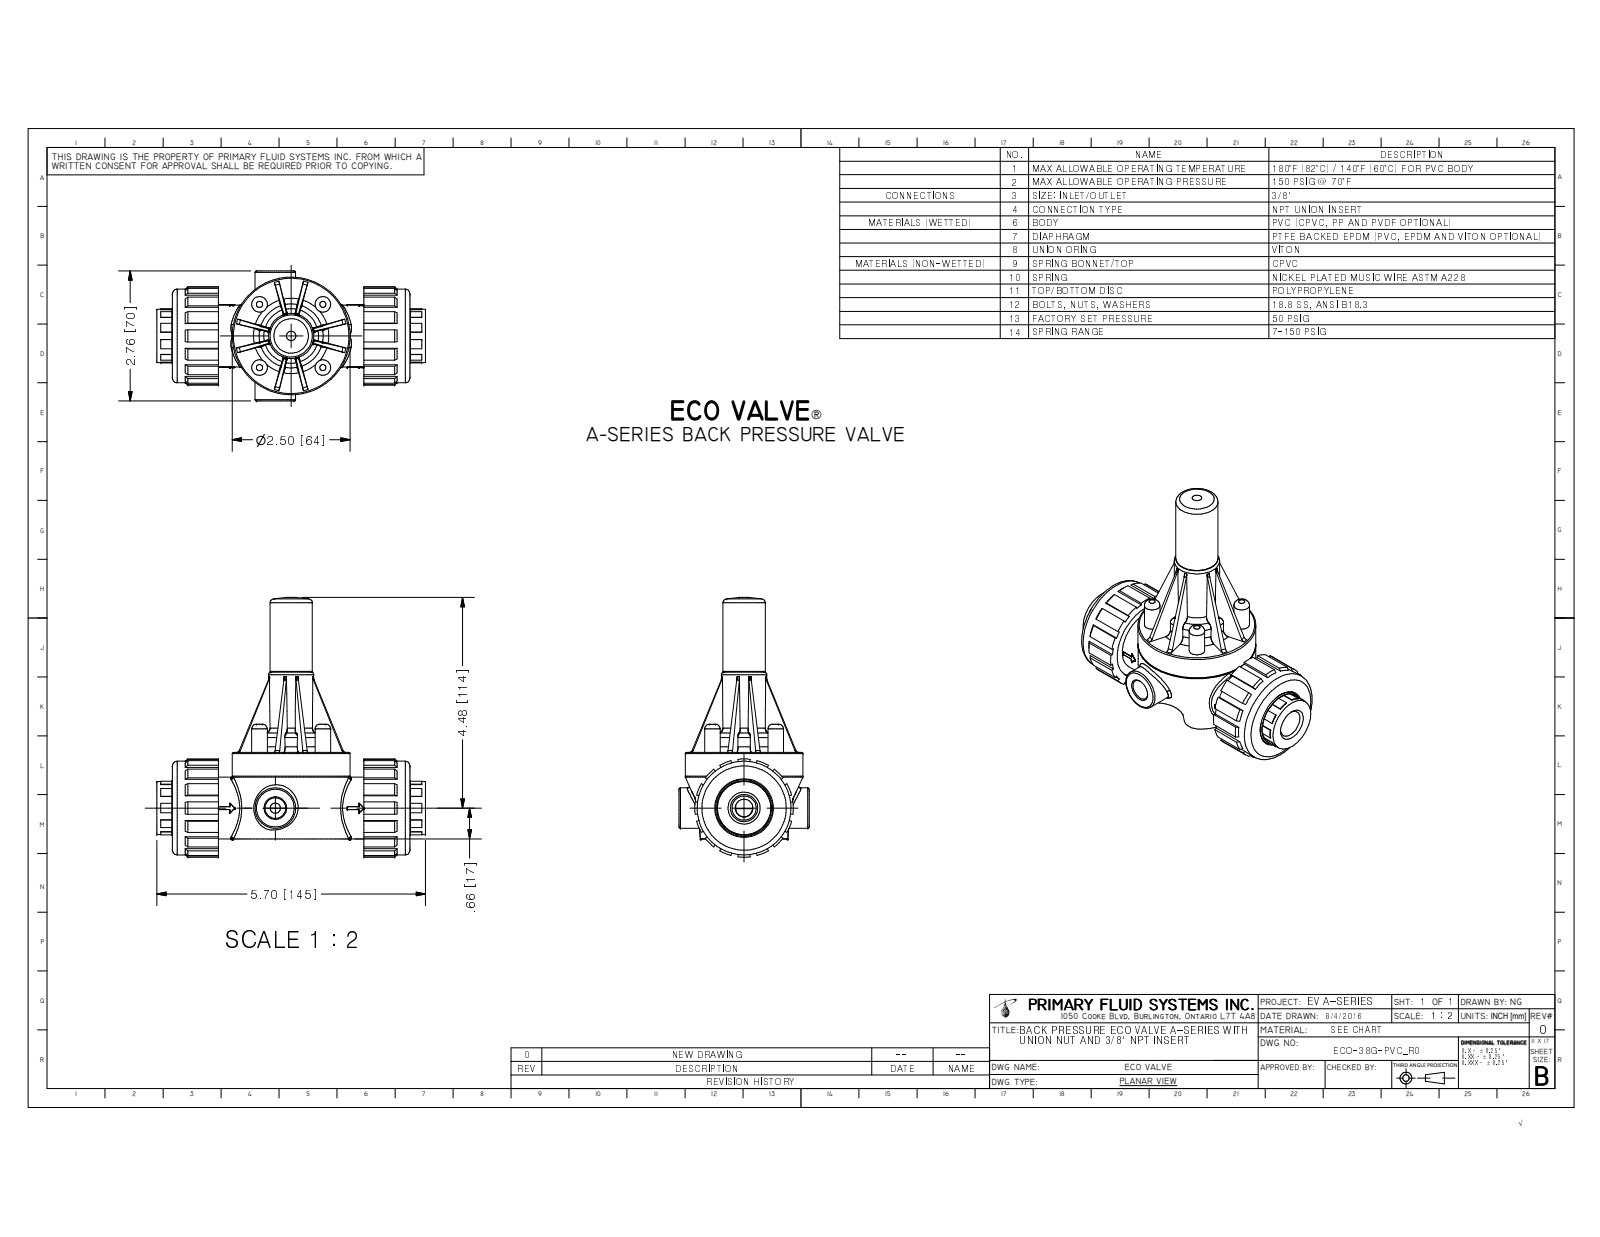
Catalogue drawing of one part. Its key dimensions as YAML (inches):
part_name: "ECO-38G-PVC_R0"
step_written_by: "Autodesk Inventor 2009 (AUTOMOTIVE_DESIGN)"
units: inches
bodies: {solids: 1, faces: 881, planar: 290, cylindrical: 188, other: 403}
overall_size: [5.7, 5.521, 2.764]
volume: 18.42
surface_area: 107.8
round_holes:
  - {diameter: 0.23, count: 4}
  - {diameter: 0.257, count: 4}
  - {diameter: 0.4, count: 4}
  - {diameter: 0.437, count: 1}
  - {diameter: 0.578, count: 1}
  - {diameter: 1.022, count: 1}
  - {diameter: 1.376, count: 1}
round_bosses_or_shafts:
  - {diameter: 0.33, count: 4}
  - {diameter: 0.256, count: 4}
  - {diameter: 2.5, count: 1}
  - {diameter: 1.69, count: 1}
  - {diameter: 1.49, count: 1}
  - {diameter: 1.36, count: 1}
  - {diameter: 1.313, count: 1}
  - {diameter: 1.205, count: 1}
partial_cylinders:
  - {radius: 0.07, count: 8}
  - {radius: 0.1, count: 8}
  - {radius: 0.128, count: 4}
  - {radius: 0.254, count: 4}
  - {radius: 0.292, count: 4}
  - {radius: 0.507, count: 1}
  - {radius: 0.575, count: 1}
  - {radius: 0.666, count: 1}
face_to_face_distances: [1.838, 0.75, 4.95, 4.2, 0.839, 4.861, 0.089, 4.111, 5.7, 1.313]
hole_center_spacings: [1.344, 1.344, 1.344, 1.9, 1.901, 1.343, 1.9, 1.902]
